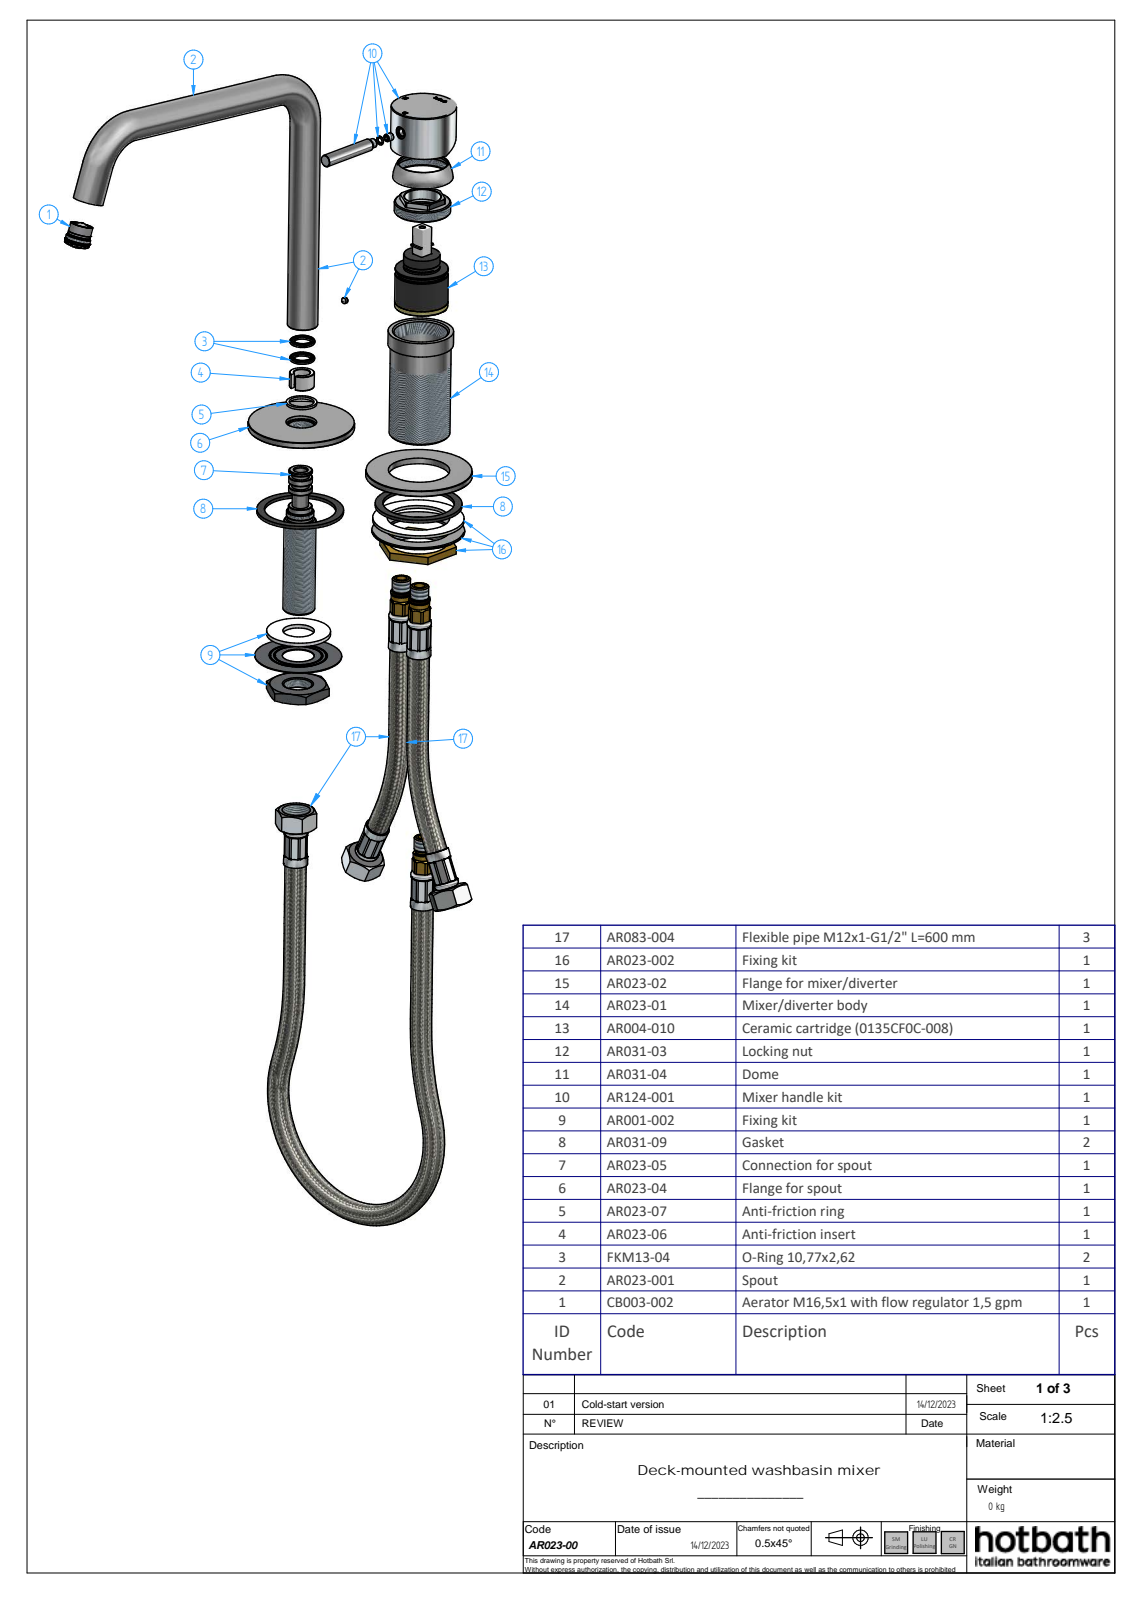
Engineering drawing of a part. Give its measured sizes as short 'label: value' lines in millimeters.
name: AR023-00 rel1; AR031-04; AR124-001_oa_0; AR031-08 (+8 more)
written by: Solid Edge (AUTOMOTIVE_DESIGN)
unit: mm
bodies: 12 solids, 320 faces (174 planar, 71 cylindrical, 75 other)
size: 244.4 × 207.63 × 180
volume: 106 818 mm³; area: 78 841 mm²
holes: 3× ⌀15, 2× ⌀57, 1× ⌀3.24, 1× ⌀4.2, 1× ⌀5.1, 1× ⌀8.2, 1× ⌀10, 1× ⌀11.03, 1× ⌀12.2, 1× ⌀14.58, 1× ⌀15.42, 1× ⌀16
bosses: 3× ⌀20, 2× ⌀70, 2× ⌀47, 1× ⌀43, 1× ⌀21, 1× ⌀18, 1× ⌀16.5, 1× ⌀15.23
rounds: 2× R0.24, 2× R0.39, 2× R0.44, 2× R0.69, 1× R0.62, 1× R0.62, 1× R0.63, 1× R0.63
face distances: 4, 1.7, 2.3, 40.1, 44.1, 42.4, 9.5, 21.6, 9, 35.1
hole spacings: 110, 112.1
